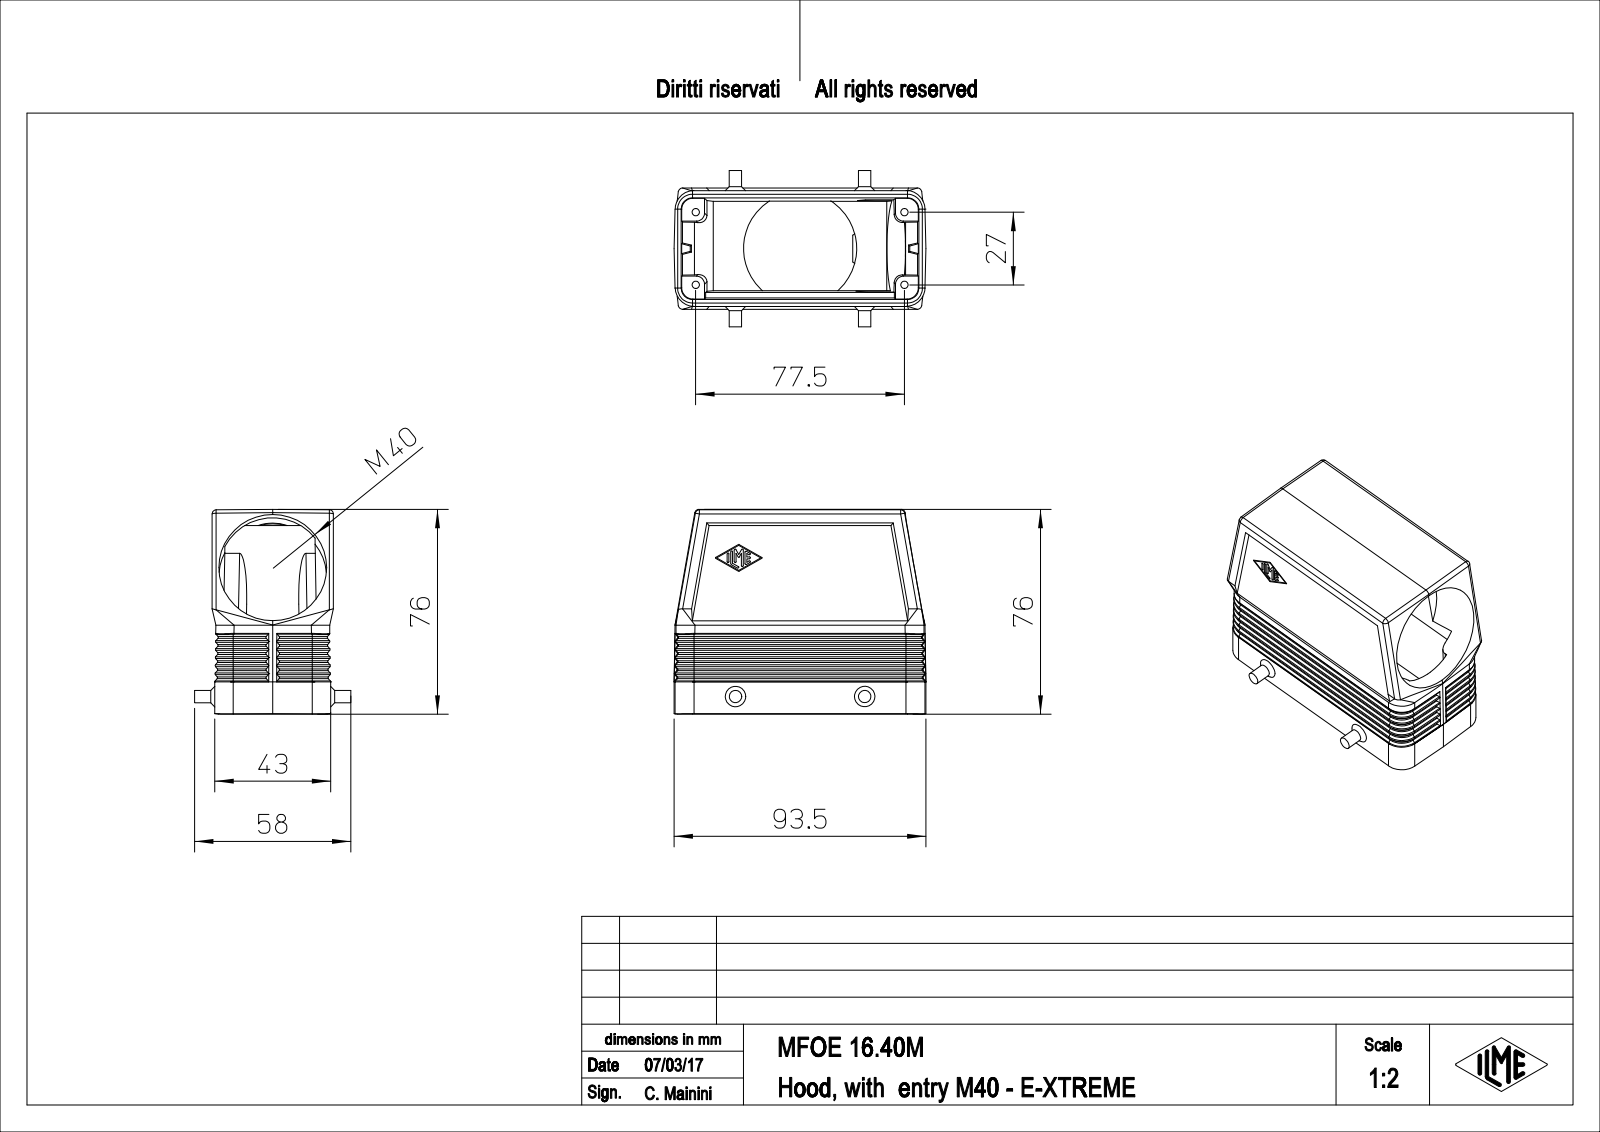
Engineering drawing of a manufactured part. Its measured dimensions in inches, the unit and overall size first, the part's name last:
Units: inches
Overall size (bounding box): 3.681 × 2.992 × 2.283
Round holes (diameter × count): ⌀0.108 ×4, ⌀1.575 ×1
Round bosses / shafts (diameter × count): ⌀0.181 ×2
Partial cylindrical surfaces — rounded edges, fillets, slot ends (radius × count): R0.02 ×78, R0.059 ×10, R0.276 ×8, R0.118 ×4, R0.165 ×4, R0.827 ×1
Main face-to-face distances: 1.693, 0.079, 0.079, 0.335, 0.157, 0.126, 0.039, 1.732, 0.236, 0.237
Hole centre spacings: 1.063, 3.051, 3.231
Volume: 5.093 in³ · Surface area: 67 in²
Bodies: 1 solid, 481 faces (212 planar, 133 cylindrical, 136 other)
Part name (STEP PRODUCT): MFOE_16.40M
STEP written by: PTC Creo Elements/Direct Modeling 19.0E 27-Jun-2016 (C) Parametric Technology GmbH (AUTOMOTIVE_DESIGN)
